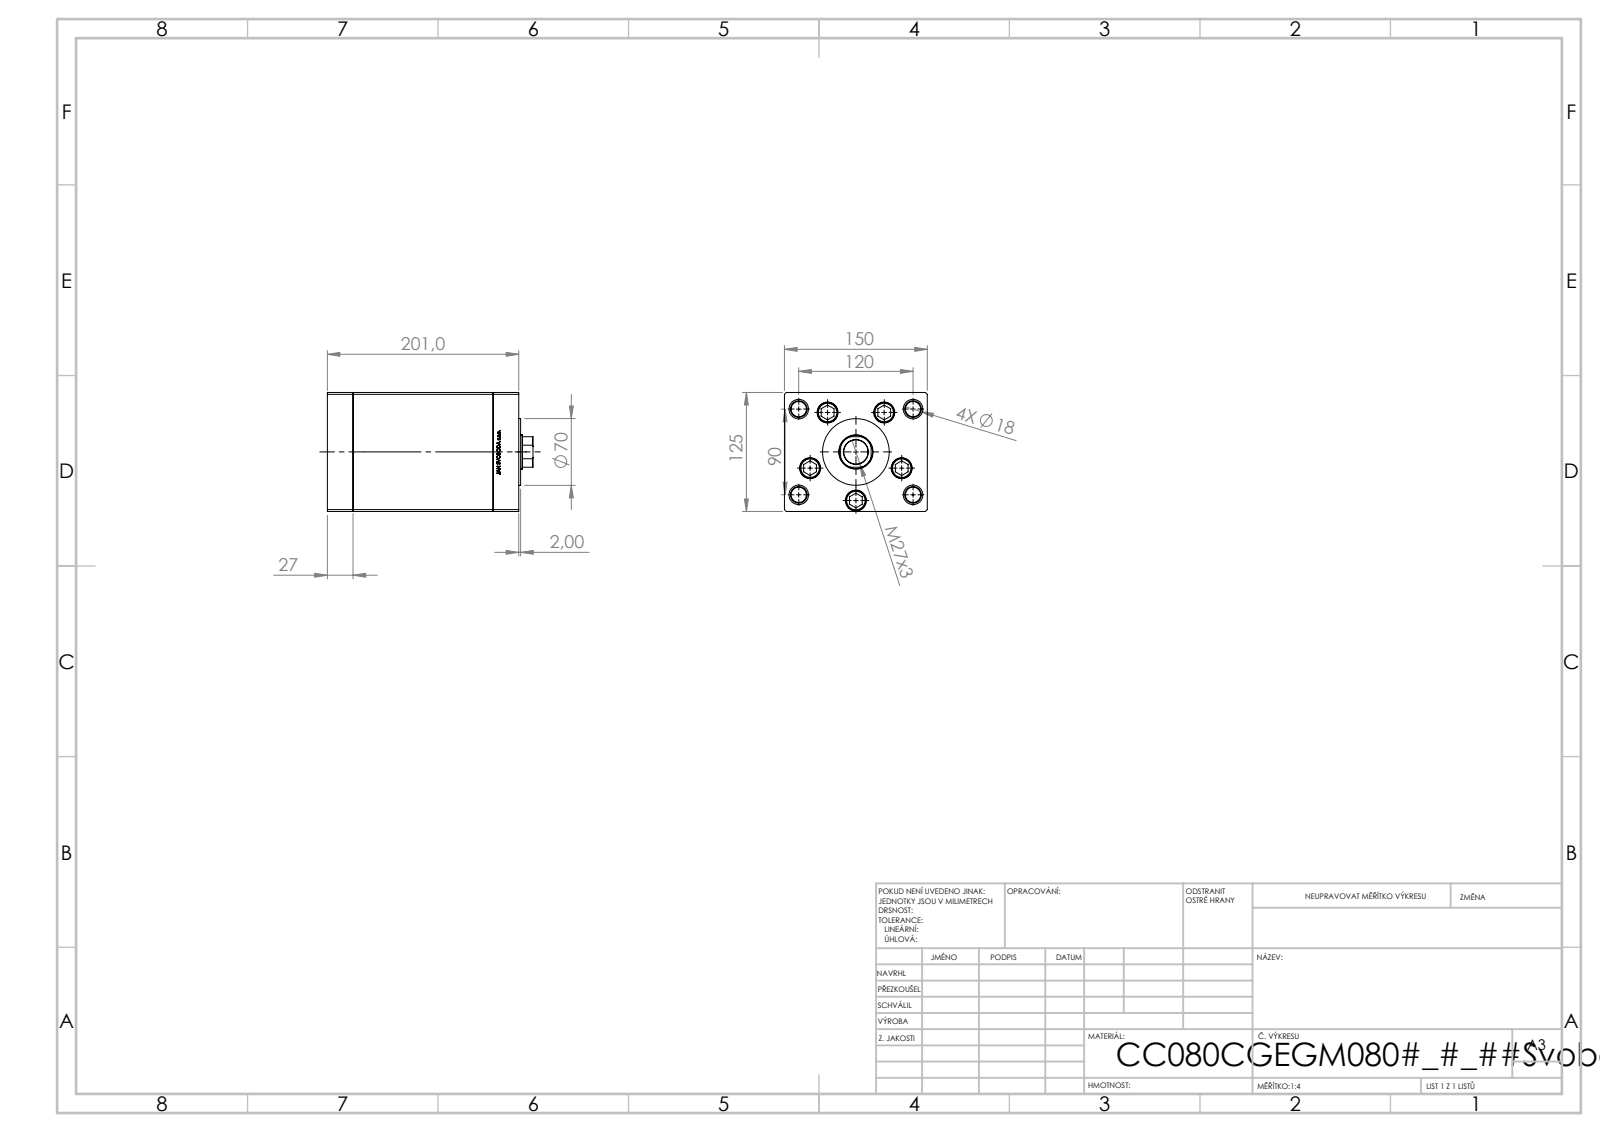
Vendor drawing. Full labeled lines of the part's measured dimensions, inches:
Part name (STEP PRODUCT): V220C FRONT; ALLEN BOLT; V220C_C MIDDLE; V220C BACK_C (+1 more)
STEP written by: SolidWorks 2019 (CONFIG_CONTROL_DESIGN)
Units: inches
Bodies: 13 solids, 1159 faces (538 planar, 159 cylindrical, 462 other)
Overall size (bounding box): 8.504 × 5.906 × 4.921
Volume: 190.8 in³ · Surface area: 587.2 in²
Round holes (diameter × count): ⌀0.689 ×9, ⌀0.866 ×5, ⌀0.63 ×4, ⌀0.807 ×4, ⌀0.827 ×1, ⌀1.004 ×1, ⌀1.417 ×1
Round bosses / shafts (diameter × count): ⌀0.315 ×5, ⌀0.827 ×4, ⌀3.15 ×1, ⌀2.756 ×1
Partial cylindrical surfaces — rounded edges, fillets, slot ends (radius × count): R0.037 ×2, R0.689 ×1
Main face-to-face distances: 1.063, 6.85, 5.787, 4.921, 5.906, 1.319, 7.913, 0.256, 6.594, 5.531
Hole centre spacings: 2.008, 2.953, 1.198, 1.2, 2.319, 2.374, 2.411, 2.486
